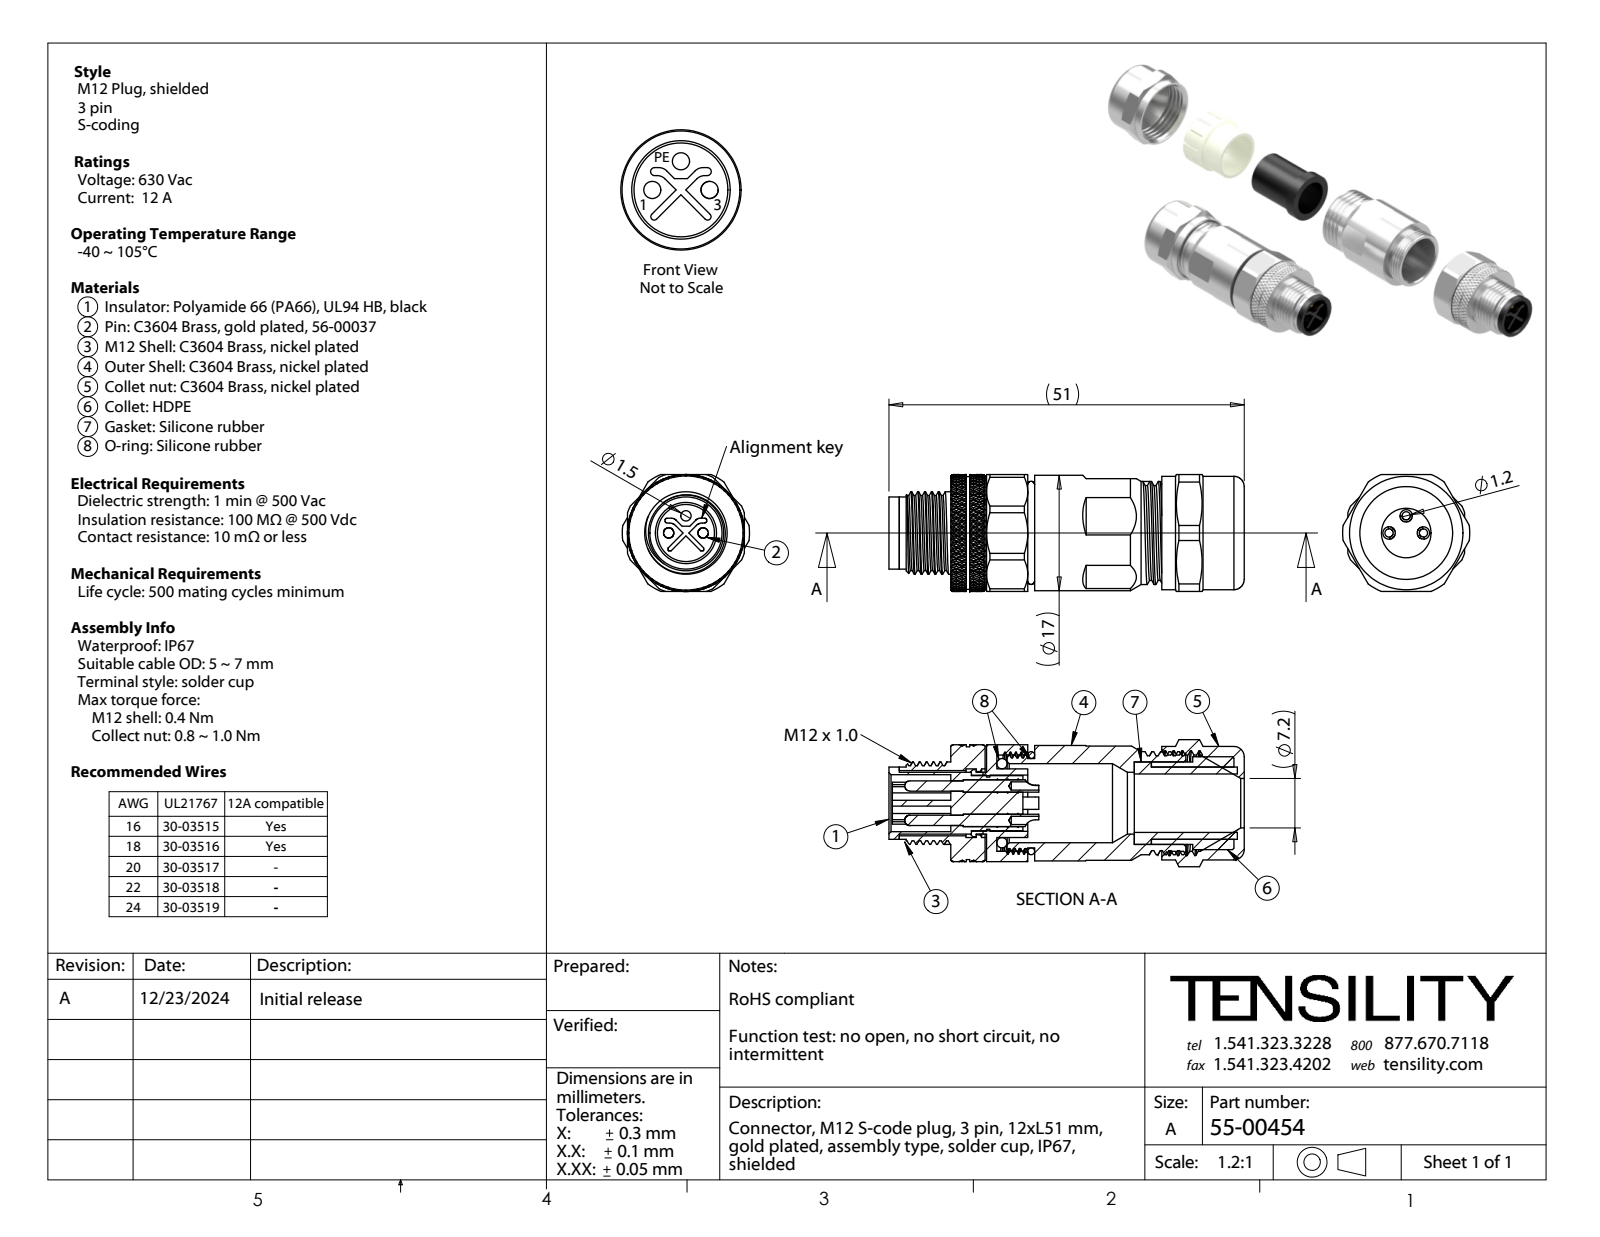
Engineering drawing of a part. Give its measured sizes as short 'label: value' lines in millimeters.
name: 55-00454-07; 55-00454-09; 55-00454-11L; 55-00454-11 (+8 more)
written by: SolidWorks 2021 (CONFIG_CONTROL_DESIGN)
unit: mm
bodies: 12 solids, 488 faces (166 planar, 192 cylindrical, 130 other)
size: 51.7 × 18.5 × 17
volume: 7 070 mm³; area: 11 148 mm²
holes: 3× ⌀1.2, 3× ⌀1.5, 1× ⌀7.2, 1× ⌀7.6, 1× ⌀8.2, 1× ⌀8.3, 1× ⌀8.5, 1× ⌀9.2, 1× ⌀9.5, 1× ⌀10, 1× ⌀11.5, 1× ⌀14
bosses: 3× ⌀1.8, 1× ⌀17, 1× ⌀16.8, 1× ⌀16.5, 1× ⌀16.4, 1× ⌀15, 1× ⌀13.5, 1× ⌀13
rounds: 3× R1.7, 2× R0.3, 2× R0.35, 2× R1, 2× R1.28, 1× R9, 1× R9.25
face distances: 17, 1.5, 5, 8.2, 6, 7.5, 1, 5.2, 30.5, 8.8
hole spacings: 2.5, 3.54, 5
